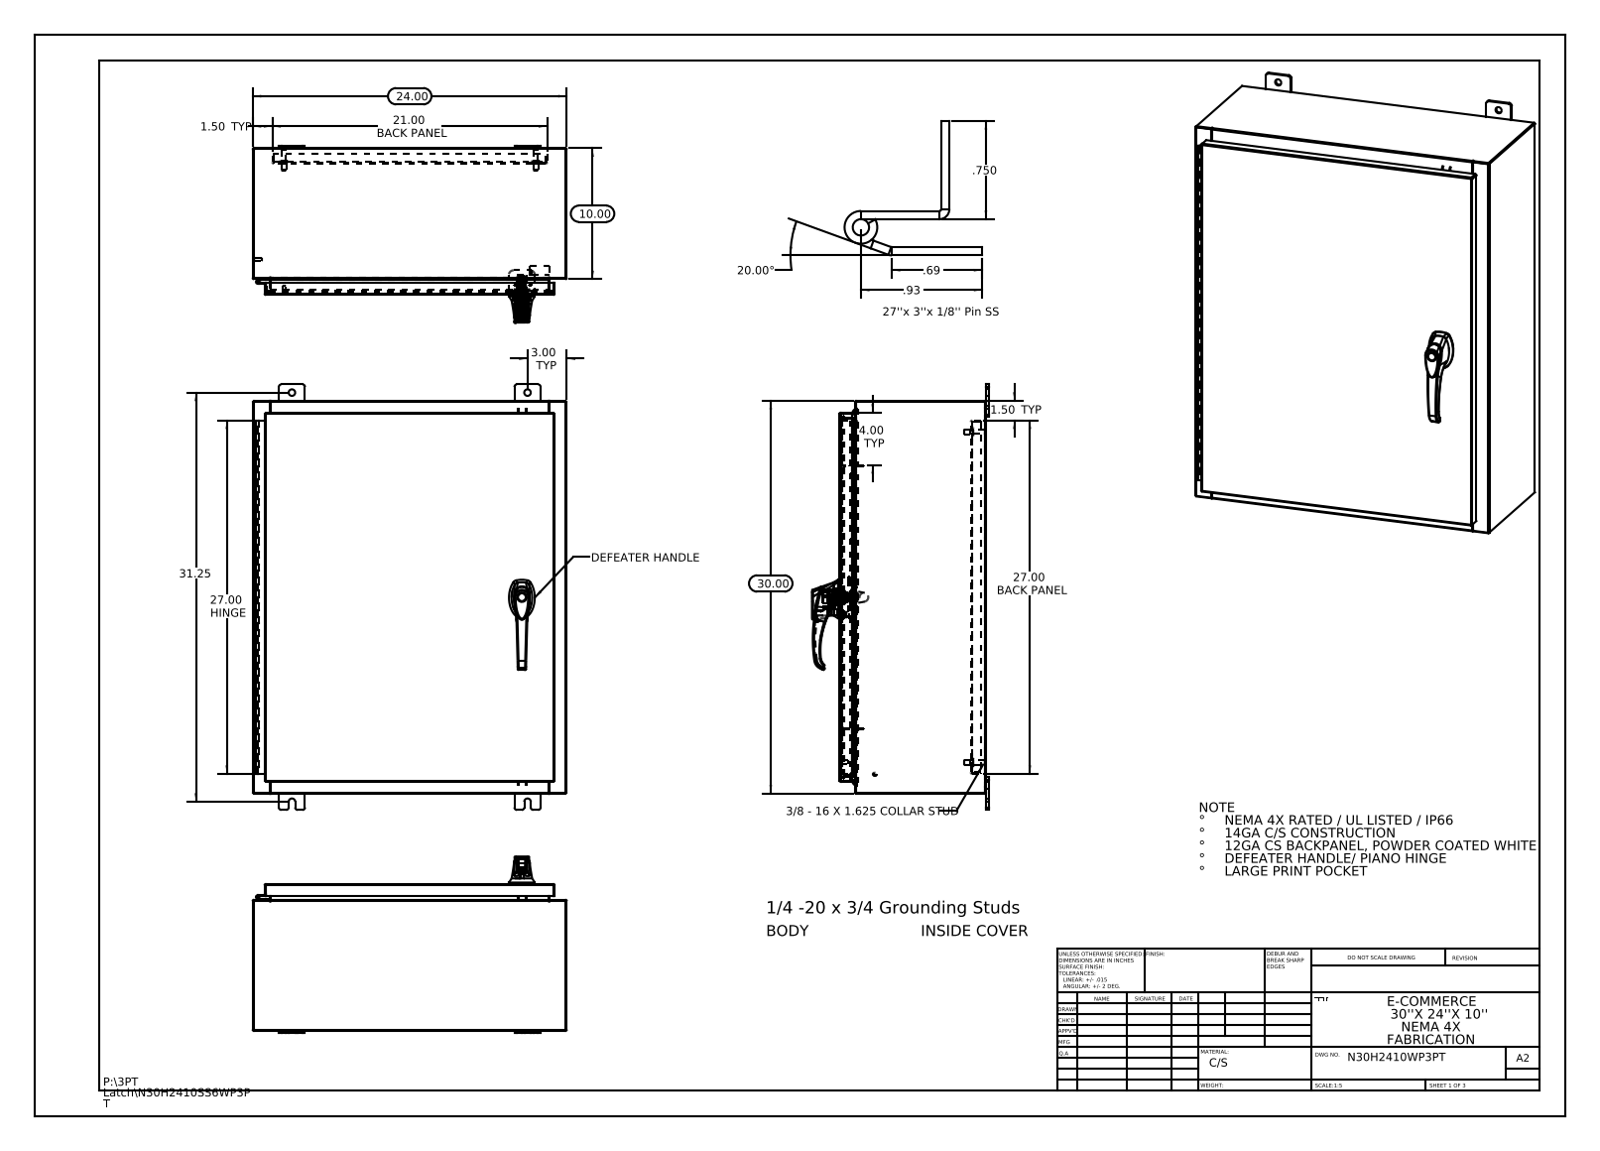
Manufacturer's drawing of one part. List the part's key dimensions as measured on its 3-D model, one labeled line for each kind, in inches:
Part name (STEP PRODUCT): 2616310101; N30H2410SS6WP3PT Mounting Studs; 033060_032151; 00005090 (+8 more)
STEP written by: SolidWorks 2013 (CONFIG_CONTROL_DESIGN)
Units: inches
Bodies: 31 solids, 2576 faces (953 planar, 969 cylindrical, 654 other)
Overall size (bounding box): 32.5 × 24 × 13.495
Volume: 288.1 in³ · Surface area: 7 143 in²
Round holes (diameter × count): ⌀0.5 ×8, ⌀0.25 ×4, ⌀0.138 ×3, ⌀0.161 ×3, ⌀0.079 ×2, ⌀0.203 ×2, ⌀0.313 ×2, ⌀0.437 ×2, ⌀0.125 ×1, ⌀0.125 ×1, ⌀0.197 ×1, ⌀0.276 ×1
Round bosses / shafts (diameter × count): ⌀0.625 ×4, ⌀0.375 ×4, ⌀0.33 ×4, ⌀1.181 ×1, ⌀0.748 ×1, ⌀0.68 ×1, ⌀0.661 ×1, ⌀0.639 ×1
Partial cylindrical surfaces — rounded edges, fillets, slot ends (radius × count): R0.118 ×37, R0.006 ×33, R0.013 ×24, R0.19 ×24, R0.088 ×18, R0.039 ×15, R0.028 ×12, R0.008 ×6
Main face-to-face distances: 0.075, 11.126, 0.104, 11.051, 11.201, 23.925, 1, 1.075, 10.051, 10.126
Hole centre spacings: 8.369, 0.295, 0.625, 0.841, 1.25, 1.313, 1.561, 1.858
